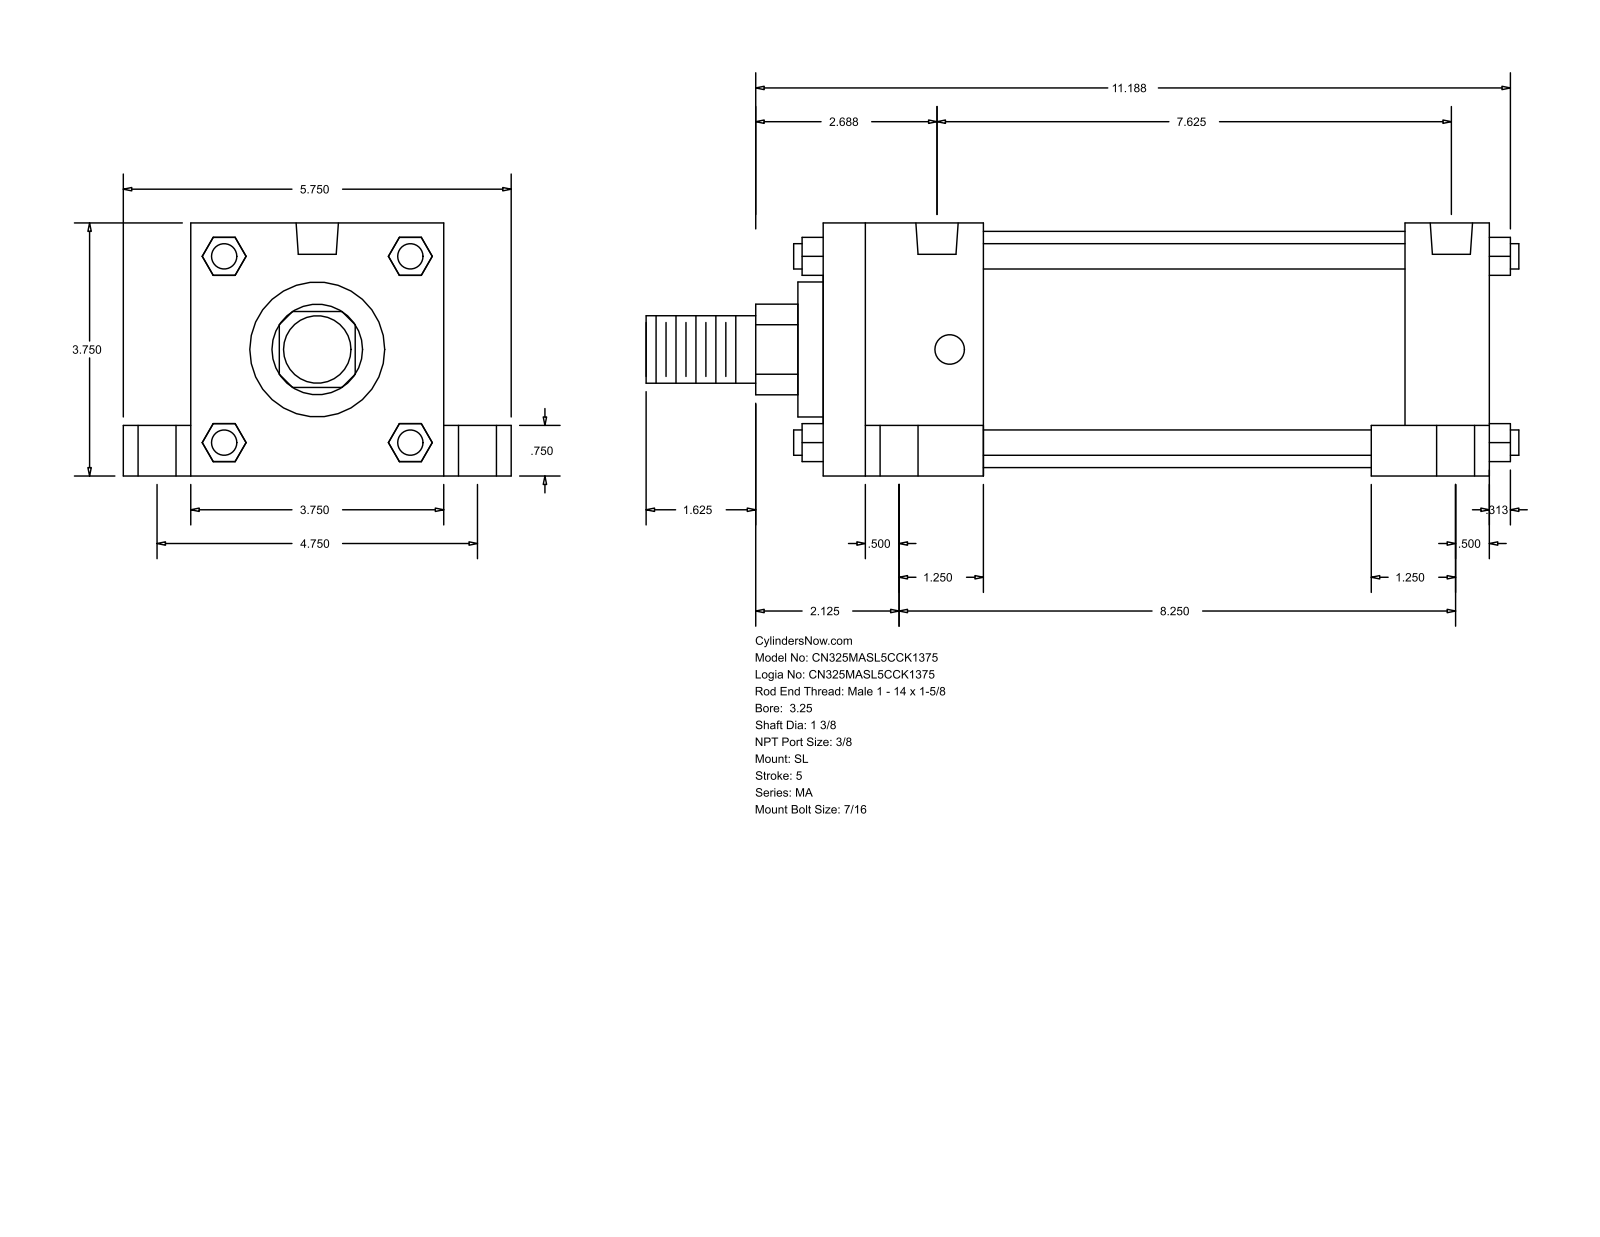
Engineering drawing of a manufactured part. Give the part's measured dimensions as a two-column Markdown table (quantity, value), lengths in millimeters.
| quantity | value |
| --- | --- |
| part name | MA_SL__0325_1.375 |
| STEP written by | GSSL Pune (CONFIG_CONTROL_DESIGN) |
| units | millimeters |
| bodies | 0 solids, 148 faces (112 planar, 36 cylindrical, 0 other) |
| overall size | 328.61 × 146.05 × 95.25 |
| round holes (diameter × count) | 11.11 × 4, 14.29 × 4, 20.64 × 4, 15.93 × 2 |
| round bosses / shafts (diameter × count) | 9.53 × 4, 88.9 × 1, 50.8 × 1, 34.92 × 1, 25.4 × 1 |
| partial cylindrical surfaces (radius × count) | 17.06 × 1 |
| main face-to-face distances | 95.24, 250.83, 158.75, 25.41, 120.65, 219.07, 31.76, 60.32, 190.51, 19.05 |
| hole center spacings | 60.35, 60.66, 62, 63.27, 120.66, 184.15, 199.82, 204.37 |
